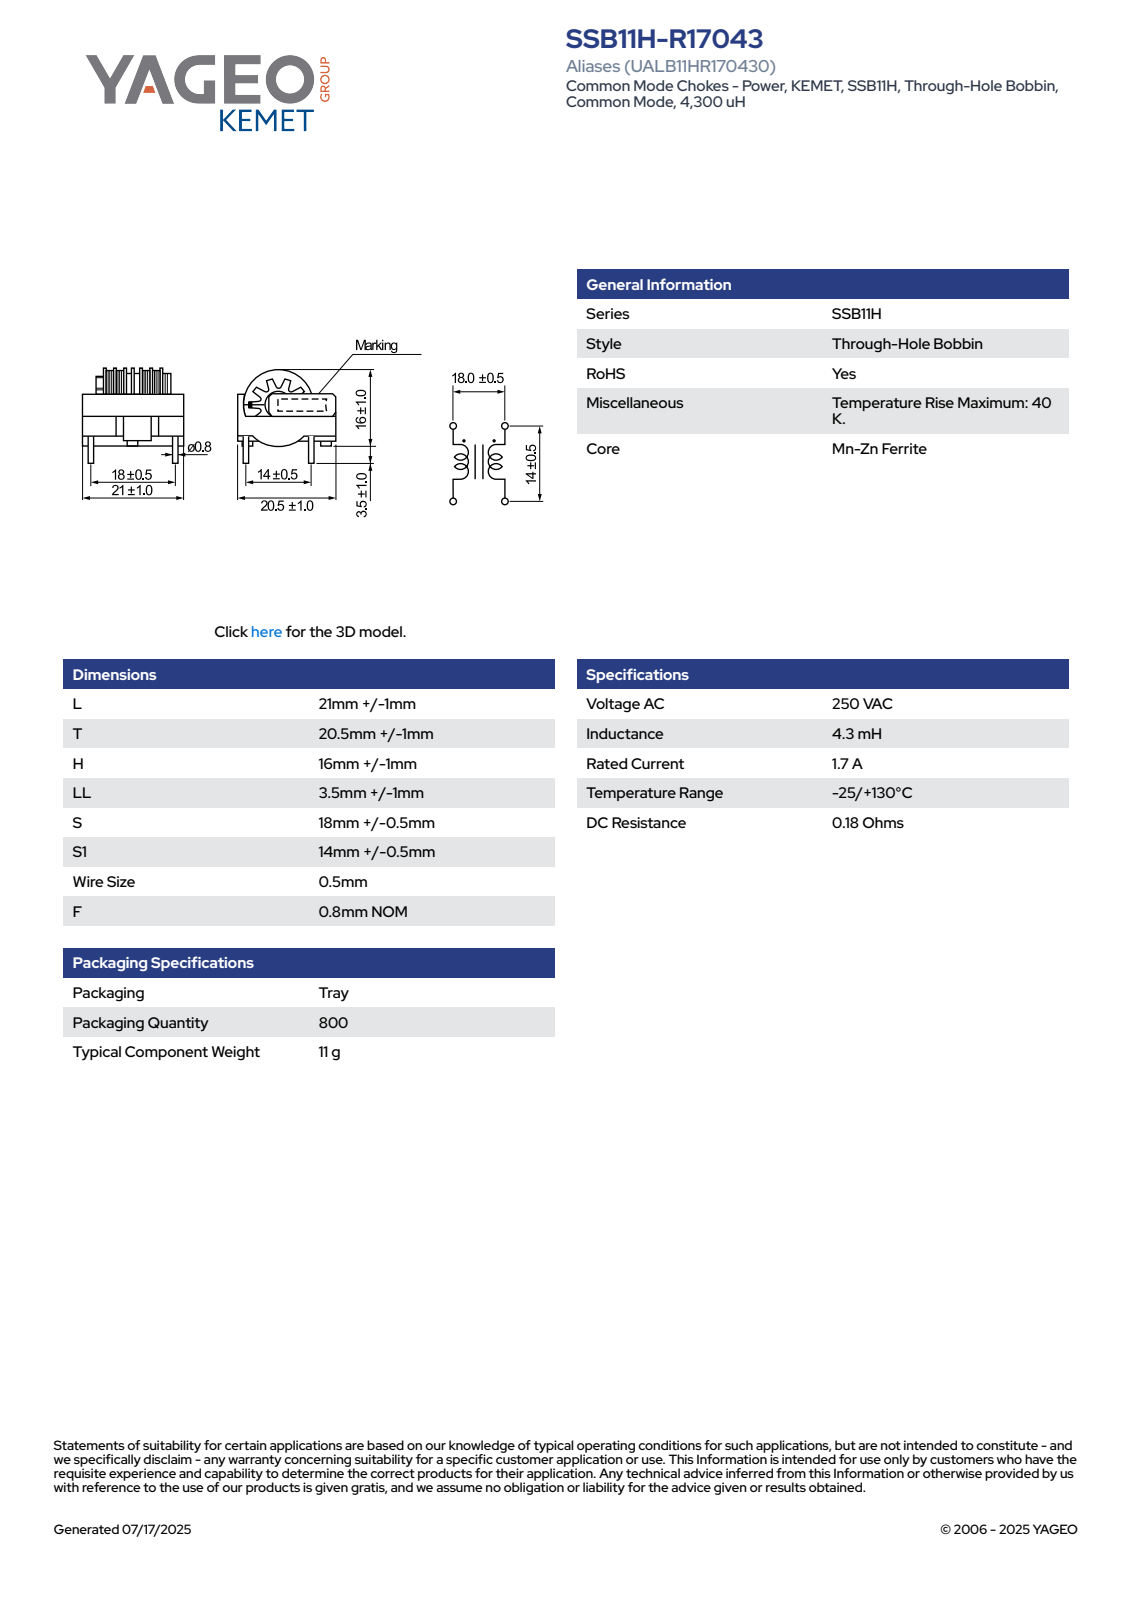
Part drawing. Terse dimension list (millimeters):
name: SSB11H(MAX-LOGO)
written by: SolidWorks 2018 (AUTOMOTIVE_DESIGN)
unit: mm
bodies: 1 solid, 426 faces (237 planar, 135 cylindrical, 54 other)
size: 22 × 21 × 20.45
volume: 4 099 mm³; area: 5 147 mm²
holes: 1× ⌀5.7, 1× ⌀6
bosses: 4× ⌀0.8, 2× ⌀2, 1× ⌀15.1, 1× ⌀12.6, 1× ⌀12.5
rounds: 20× R1.69, 14× R0.5, 8× R1, 8× R1.5, 2× R0.2, 2× R0.3, 1× R3.75, 1× R6
face distances: 4.17, 7.47, 0.6, 4.77, 7.48, 4.6, 3.2, 18.8, 3, 1.4
